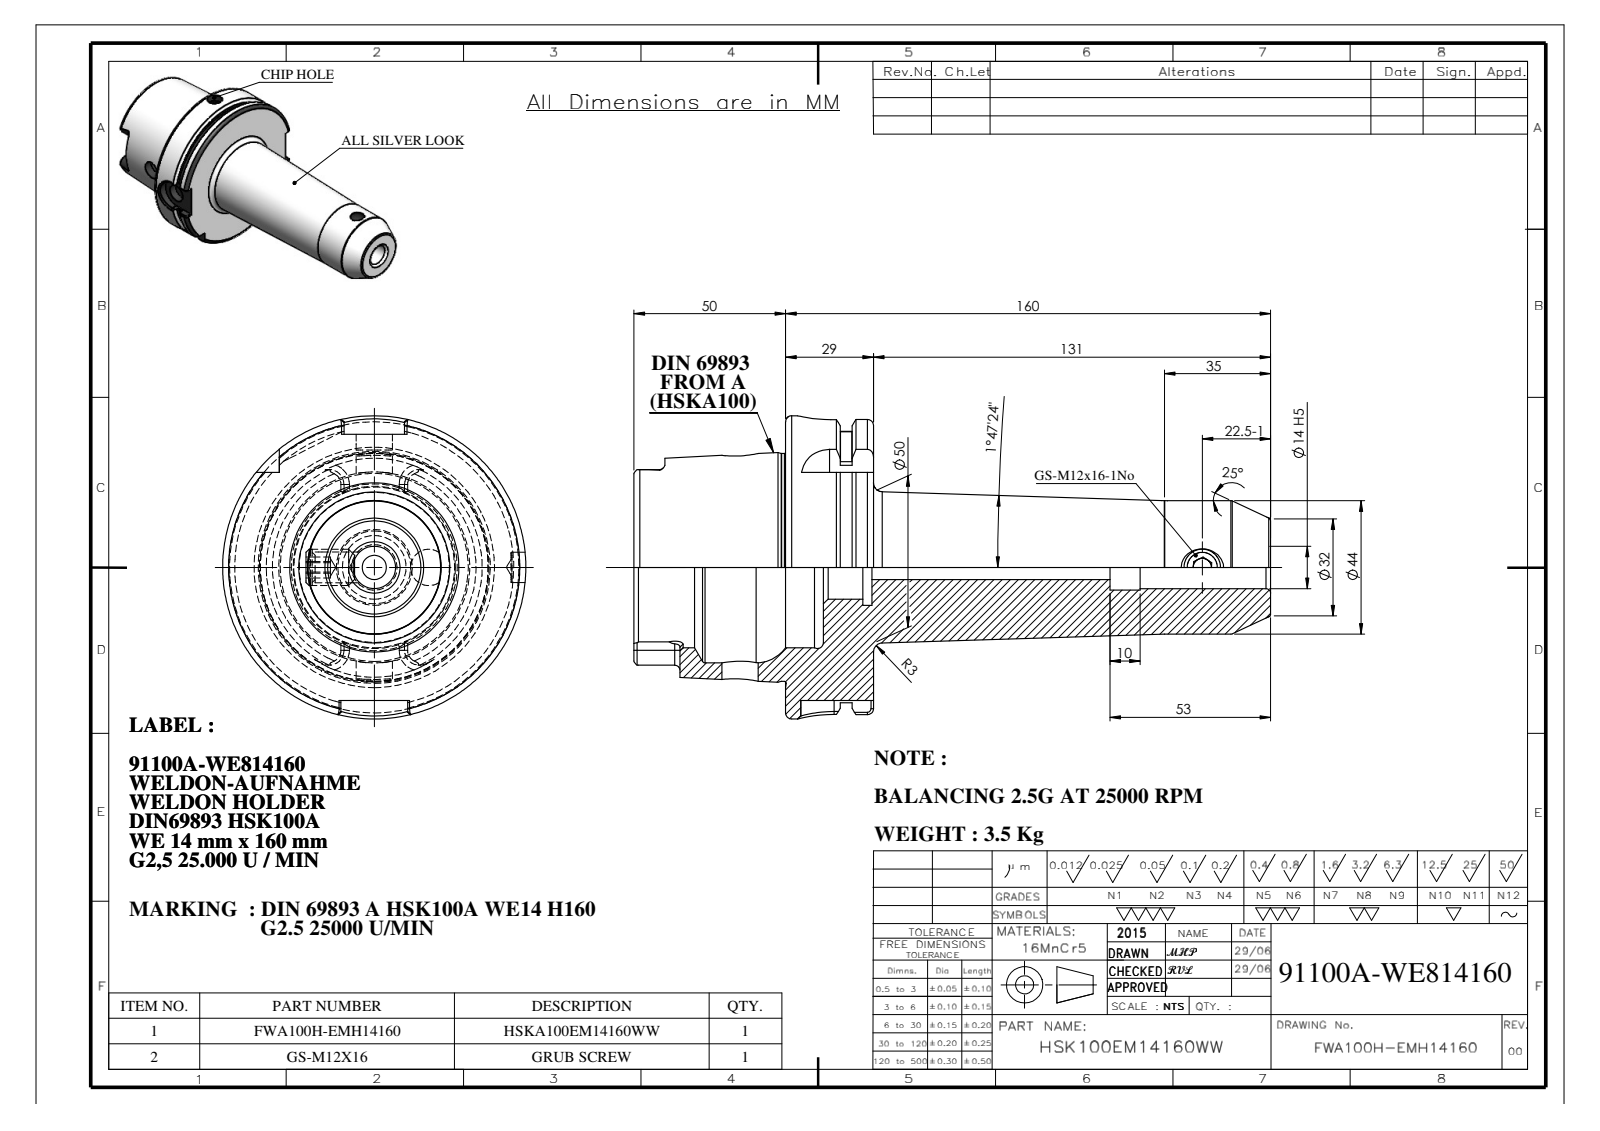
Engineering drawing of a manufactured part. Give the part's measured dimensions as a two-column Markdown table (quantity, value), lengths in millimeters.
| quantity | value |
| --- | --- |
| part name | 91100A-WE814160; GS-M12X16-DIN1835-B; HSKA100EM14160WW |
| STEP written by | SolidWorks 2018 (CONFIG_CONTROL_DESIGN) |
| units | millimeters |
| bodies | 2 solids, 218 faces (70 planar, 58 cylindrical, 90 other) |
| overall size | 210 × 100 × 100 |
| volume | 456 015 mm³ |
| surface area | 73 108 mm² |
| round holes (diameter × count) | 12 × 3, 8 × 1, 10 × 1, 10.2 × 1, 14 × 1, 15 × 1, 21 × 1, 25 × 1, 53 × 1, 63 × 1 |
| round bosses / shafts (diameter × count) | 100 × 1, 92 × 1, 75.16 × 1, 44 × 1 |
| partial cylindrical surfaces (radius × count) | 1.8 × 6, 4.88 × 4, 10 × 2, 11 × 1 |
| main face-to-face distances | 29, 12.5, 16.5, 50, 62.5, 79, 78.5, 210, 160, 147.5 |
| hole center spacings | 30, 130.5 |
